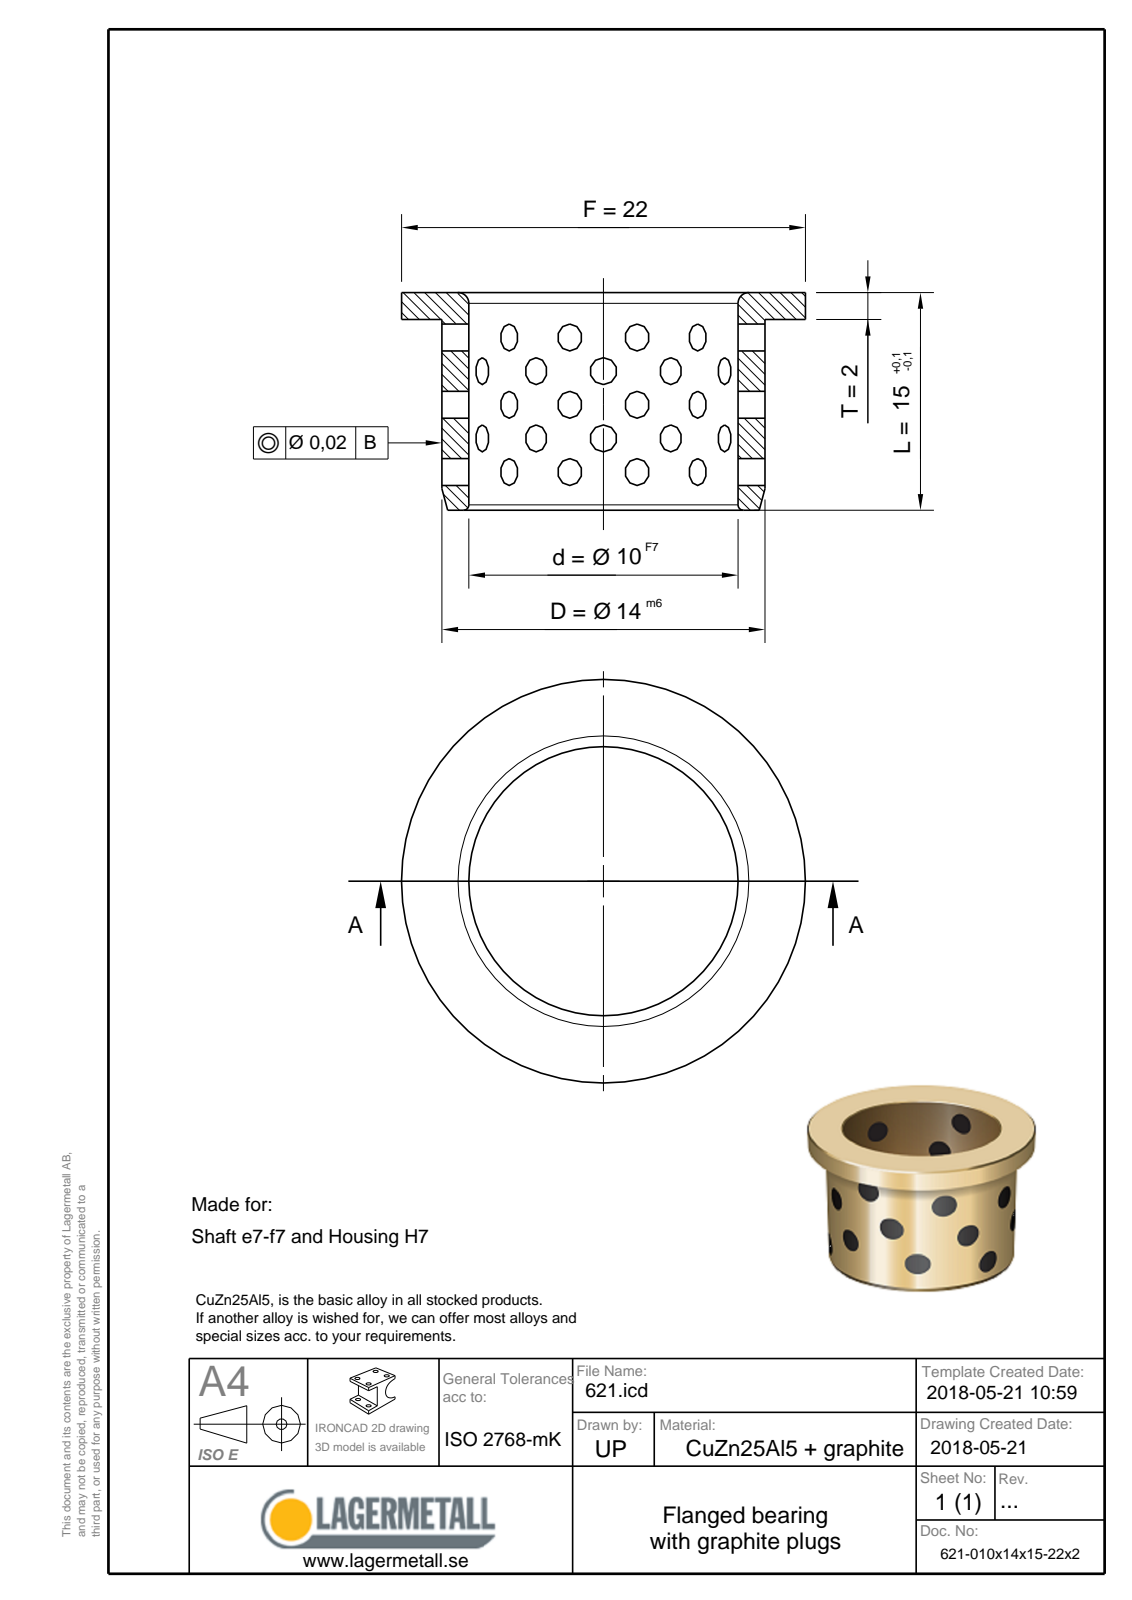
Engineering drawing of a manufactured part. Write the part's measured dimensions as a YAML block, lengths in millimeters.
part_name: "621-010x14x15-22x2"
step_written_by: "Spatial InterOp 3D (CONFIG_CONTROL_DESIGN)"
units: millimeters
bodies: {solids: 1, faces: 9, planar: 3, cylindrical: 3, other: 3}
overall_size: [22, 22, 15]
volume: 1556
surface_area: 1739
round_holes:
  - {diameter: 10, count: 1}
round_bosses_or_shafts:
  - {diameter: 22, count: 1}
  - {diameter: 14, count: 1}
face_to_face_distances: [2, 13, 15]
